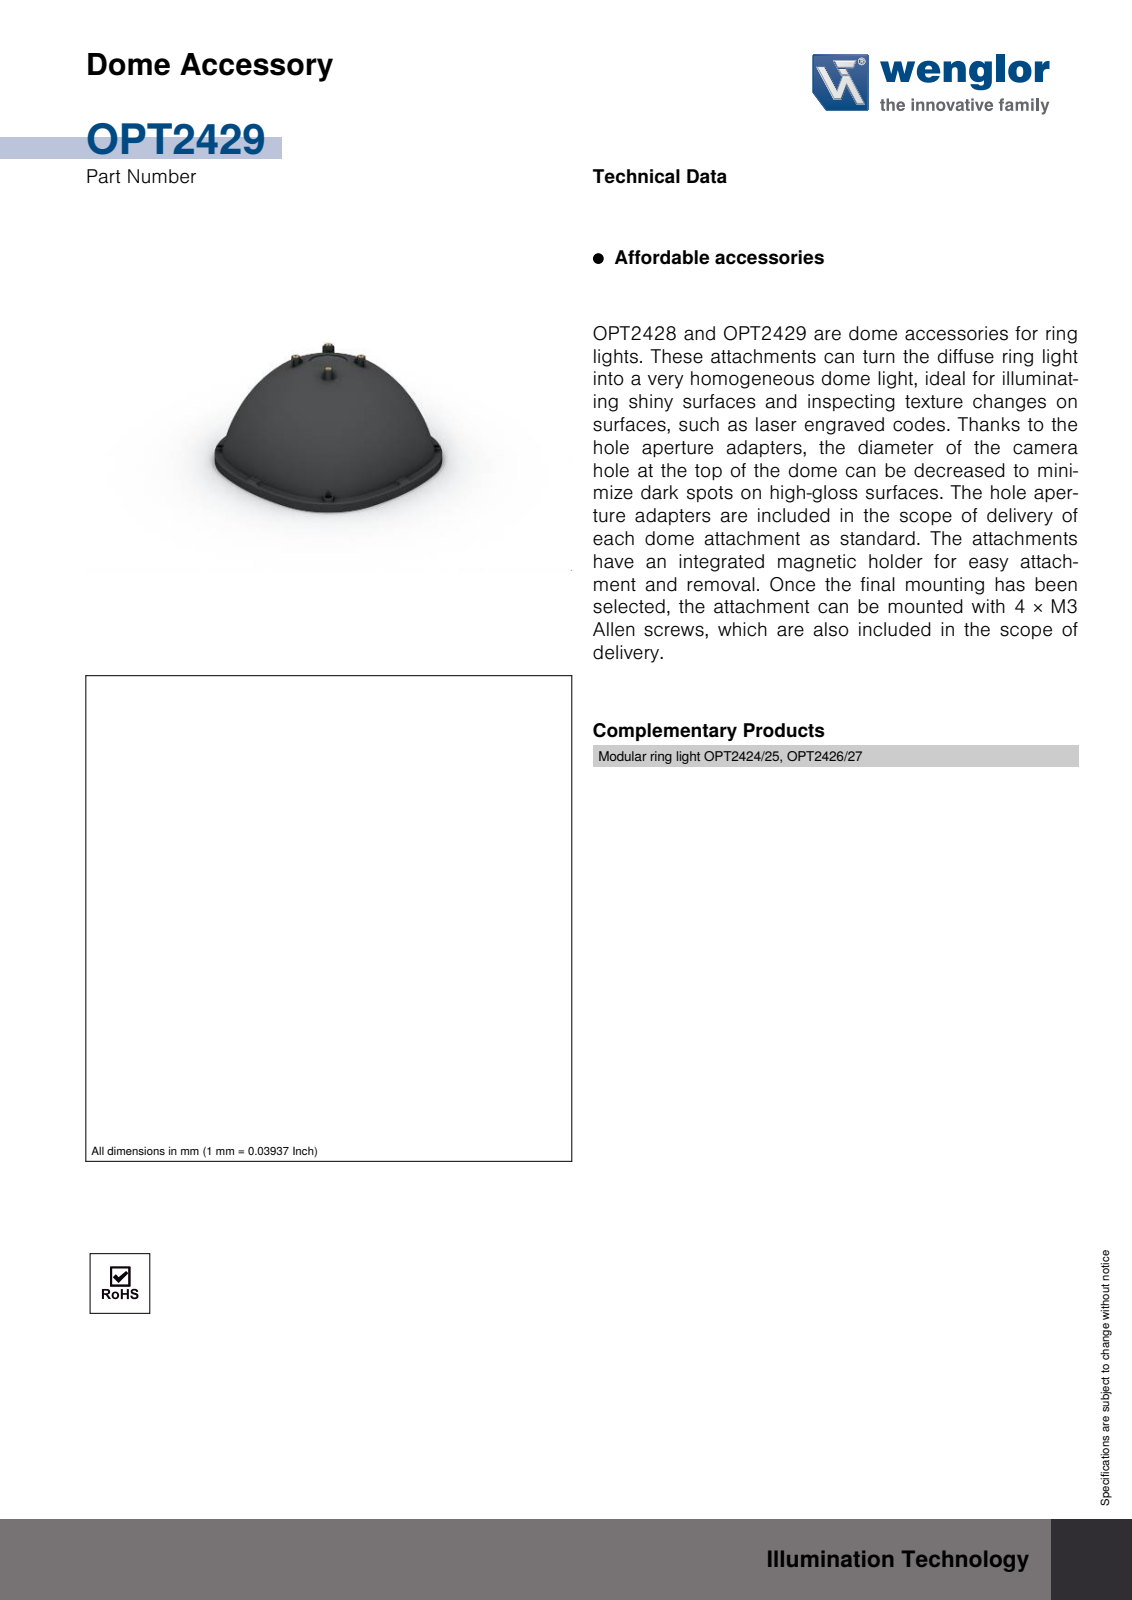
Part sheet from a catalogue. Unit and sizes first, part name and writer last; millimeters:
Units: millimetres
Overall size (bounding box): 197 × 195.4 × 102.7
Round holes (diameter × count): ⌀3 ×4, ⌀4.2 ×4
Partial cylindrical surfaces — rounded edges, fillets, slot ends (radius × count): R0.3 ×92, R1 ×16, R1.5 ×15, R0.5 ×10
Main face-to-face distances: 2, 6.8, 8.7, 94, 102.7, 96, 4, 90.7, 92, 95.7
Hole centre spacings: 42, 59.4
Volume: 118 900 mm³ · Surface area: 123 900 mm²
Bodies: 1 solid, 865 faces (137 planar, 172 cylindrical, 556 other)
Part name (STEP PRODUCT): OPT2429
STEP written by: SolidWorks 2021 (AUTOMOTIVE_DESIGN)
